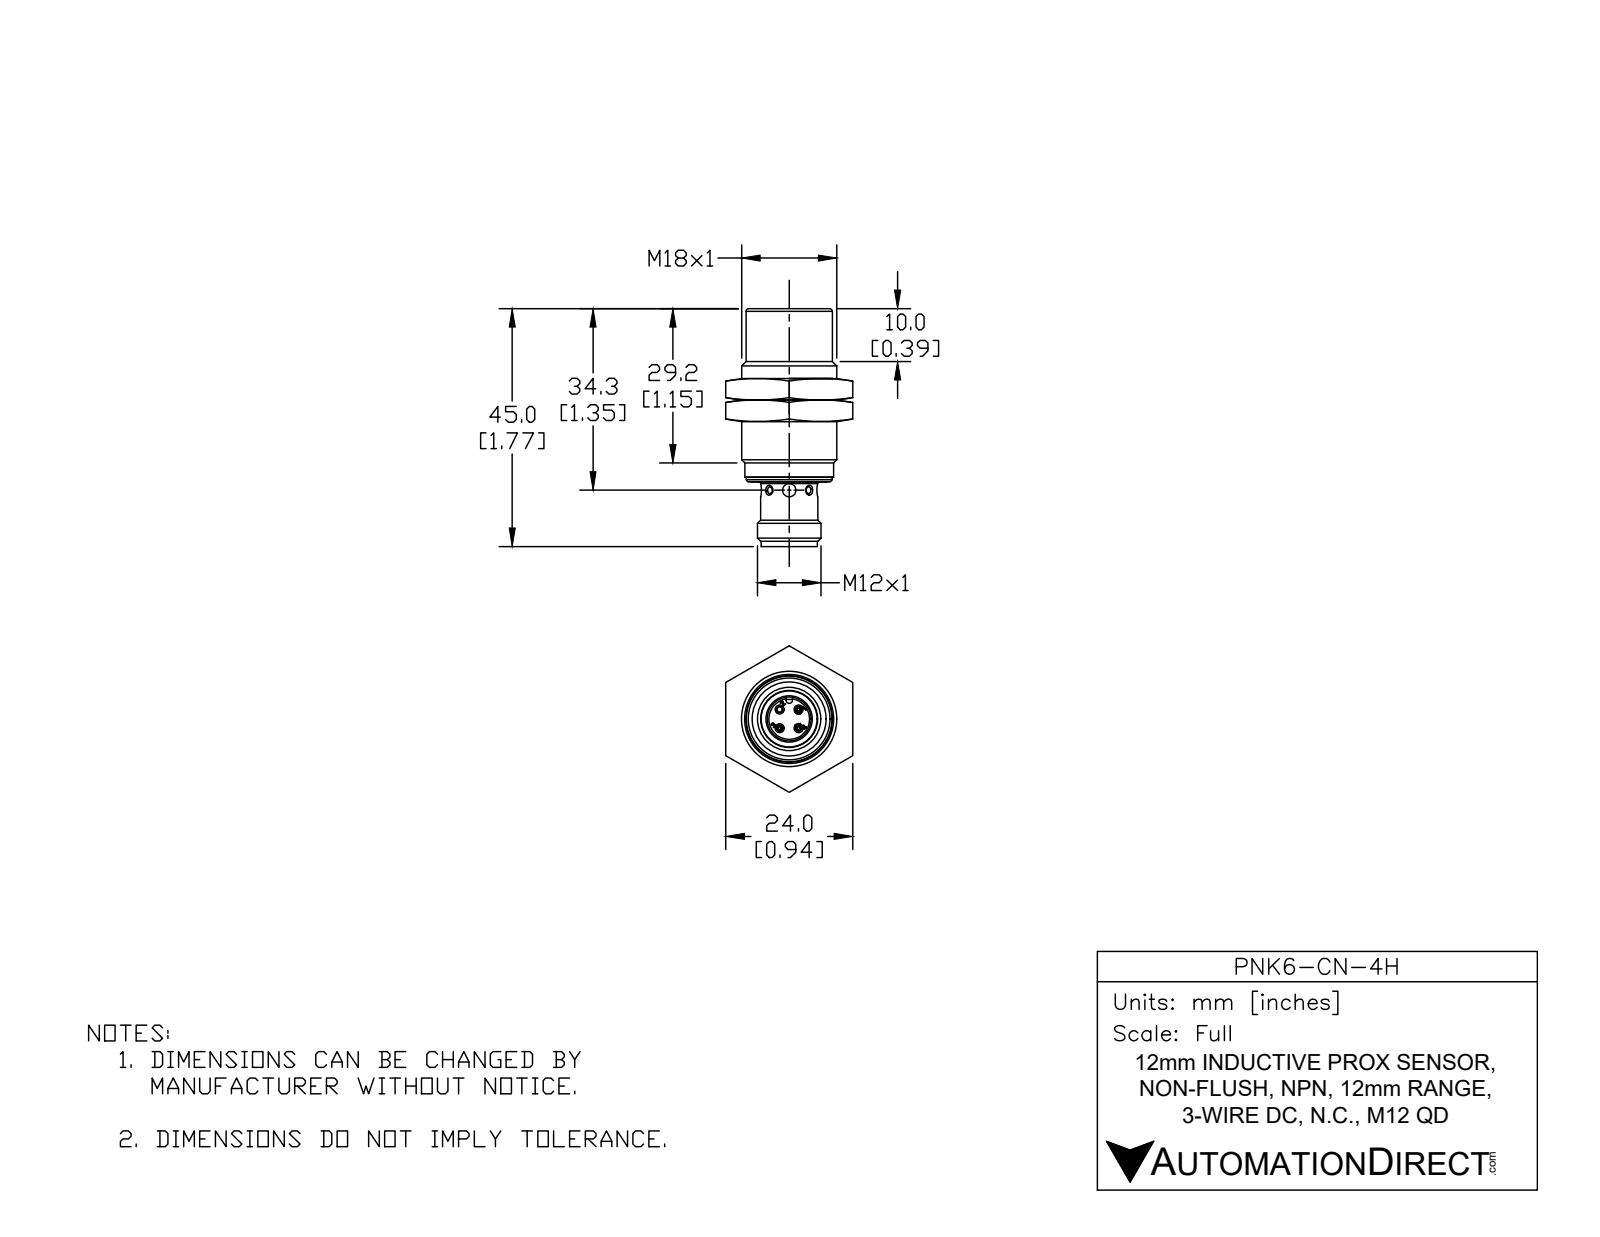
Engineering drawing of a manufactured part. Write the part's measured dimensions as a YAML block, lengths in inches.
part_name: "PNK6-CN-4H"
step_written_by: "SolidWorks 2017 (AUTOMOTIVE_DESIGN)"
units: inches
bodies: {solids: 1, faces: 476, planar: 118, cylindrical: 129, other: 229}
overall_size: [1.772, 0.709, 0.709]
volume: 0.401
surface_area: 7.642
round_holes:
  - {diameter: 0.04, count: 3}
  - {diameter: 0.043, count: 3}
  - {diameter: 0.098, count: 2}
  - {diameter: 0.038, count: 1}
  - {diameter: 0.323, count: 1}
  - {diameter: 0.327, count: 1}
  - {diameter: 0.394, count: 1}
  - {diameter: 0.618, count: 1}
round_bosses_or_shafts:
  - {diameter: 0.039, count: 9}
  - {diameter: 0.709, count: 1}
  - {diameter: 0.661, count: 1}
  - {diameter: 0.642, count: 1}
  - {diameter: 0.638, count: 1}
  - {diameter: 0.616, count: 1}
  - {diameter: 0.472, count: 1}
  - {diameter: 0.425, count: 1}
partial_cylinders:
  - {radius: 0.004, count: 24}
  - {radius: 0.039, count: 6}
  - {radius: 0.071, count: 6}
  - {radius: 0.024, count: 1}
  - {radius: 0.031, count: 1}
face_to_face_distances: [0.452, 0.03, 0.422, 1.236, 1.207, 0.785, 1.291, 0.055, 1.262, 0.84]
hole_center_spacings: [0.098, 0.139, 0.197]
